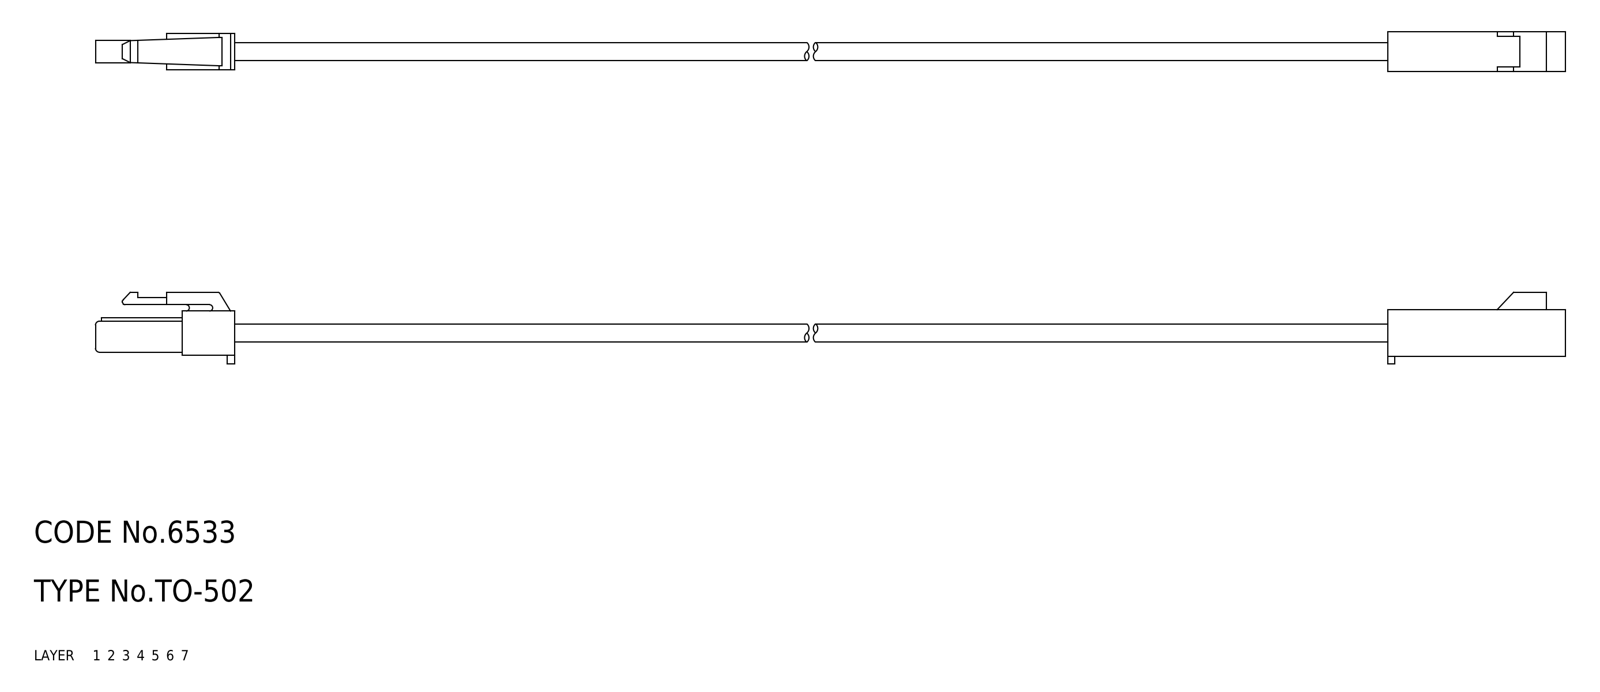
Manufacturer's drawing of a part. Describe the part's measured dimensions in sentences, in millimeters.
The part is named "67112196; 67112209; 67112222; 67112235". Its 3-D file was written by "CADfix (AUTOMOTIVE_DESIGN)". It is 4 solids with 83 faces: 0 planar, 0 cylindrical and 83 other. Overall it measures 200 by 9.72 by 5.48 millimeters. Its volume is 2 070 cubic millimeters and its surface area 2 532 square millimeters.
